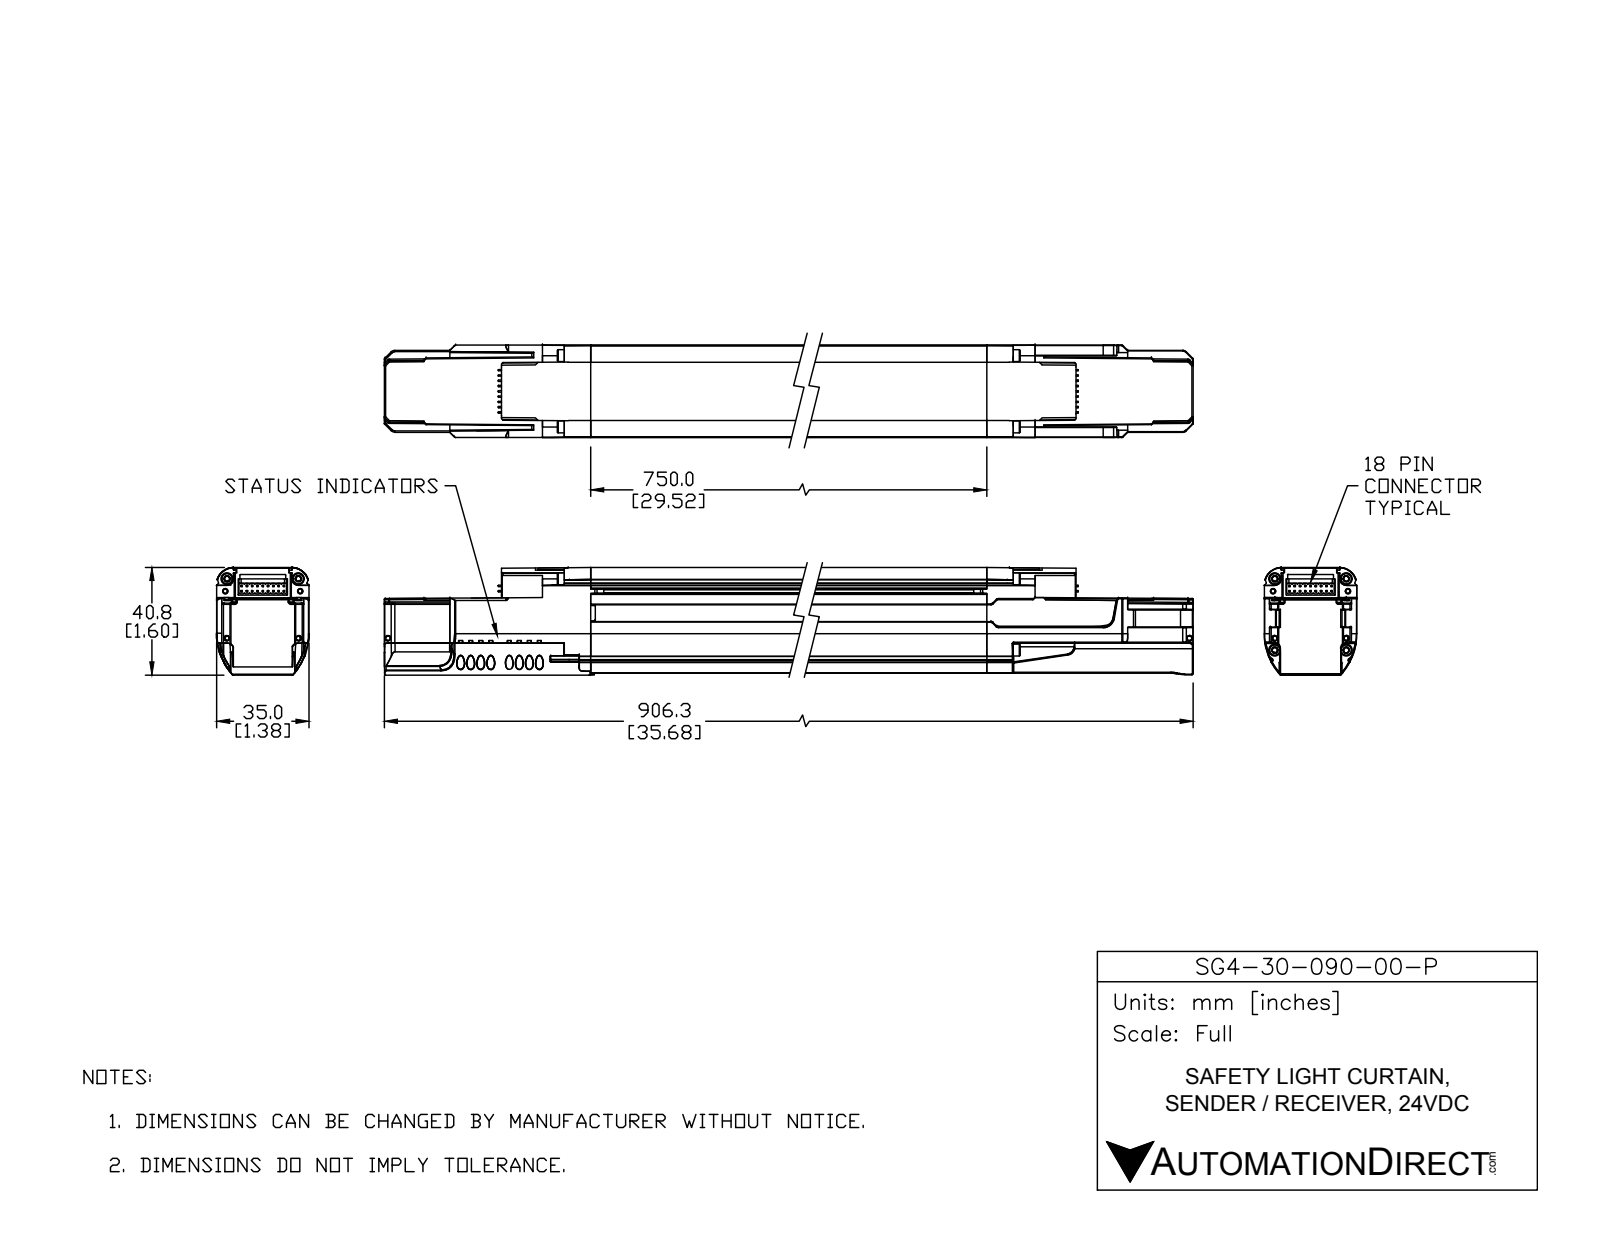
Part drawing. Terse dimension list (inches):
name: SG4-30-090-OO-P
written by: SolidWorks 2017 (AUTOMOTIVE_DESIGN)
unit: in
bodies: 16 solids, 534 faces (362 planar, 110 cylindrical, 62 other)
size: 35.673 × 2.58 × 2.023
volume: 67.38 in³; area: 381.2 in²
holes: 6× ⌀0.07, 4× ⌀0.1, 4× ⌀0.165, 4× ⌀0.209, 4× ⌀0.26, 1× ⌀0.065, 1× ⌀0.065
bosses: 4× ⌀0.394, 4× ⌀0.197
rounds: 16× R0.106, 8× R0.118, 4× R0.1, 4× R0.11, 2× R0.08, 2× R0.12, 2× R0.123, 2× R0.125
face distances: 0.06, 0.084, 0.024, 1.49, 1.466, 1.55, 1.057, 0.481, 0.985, 1.009
hole spacings: 0.569, 27.945, 0.02, 0.204, 0.207, 0.207, 0.227, 0.71
